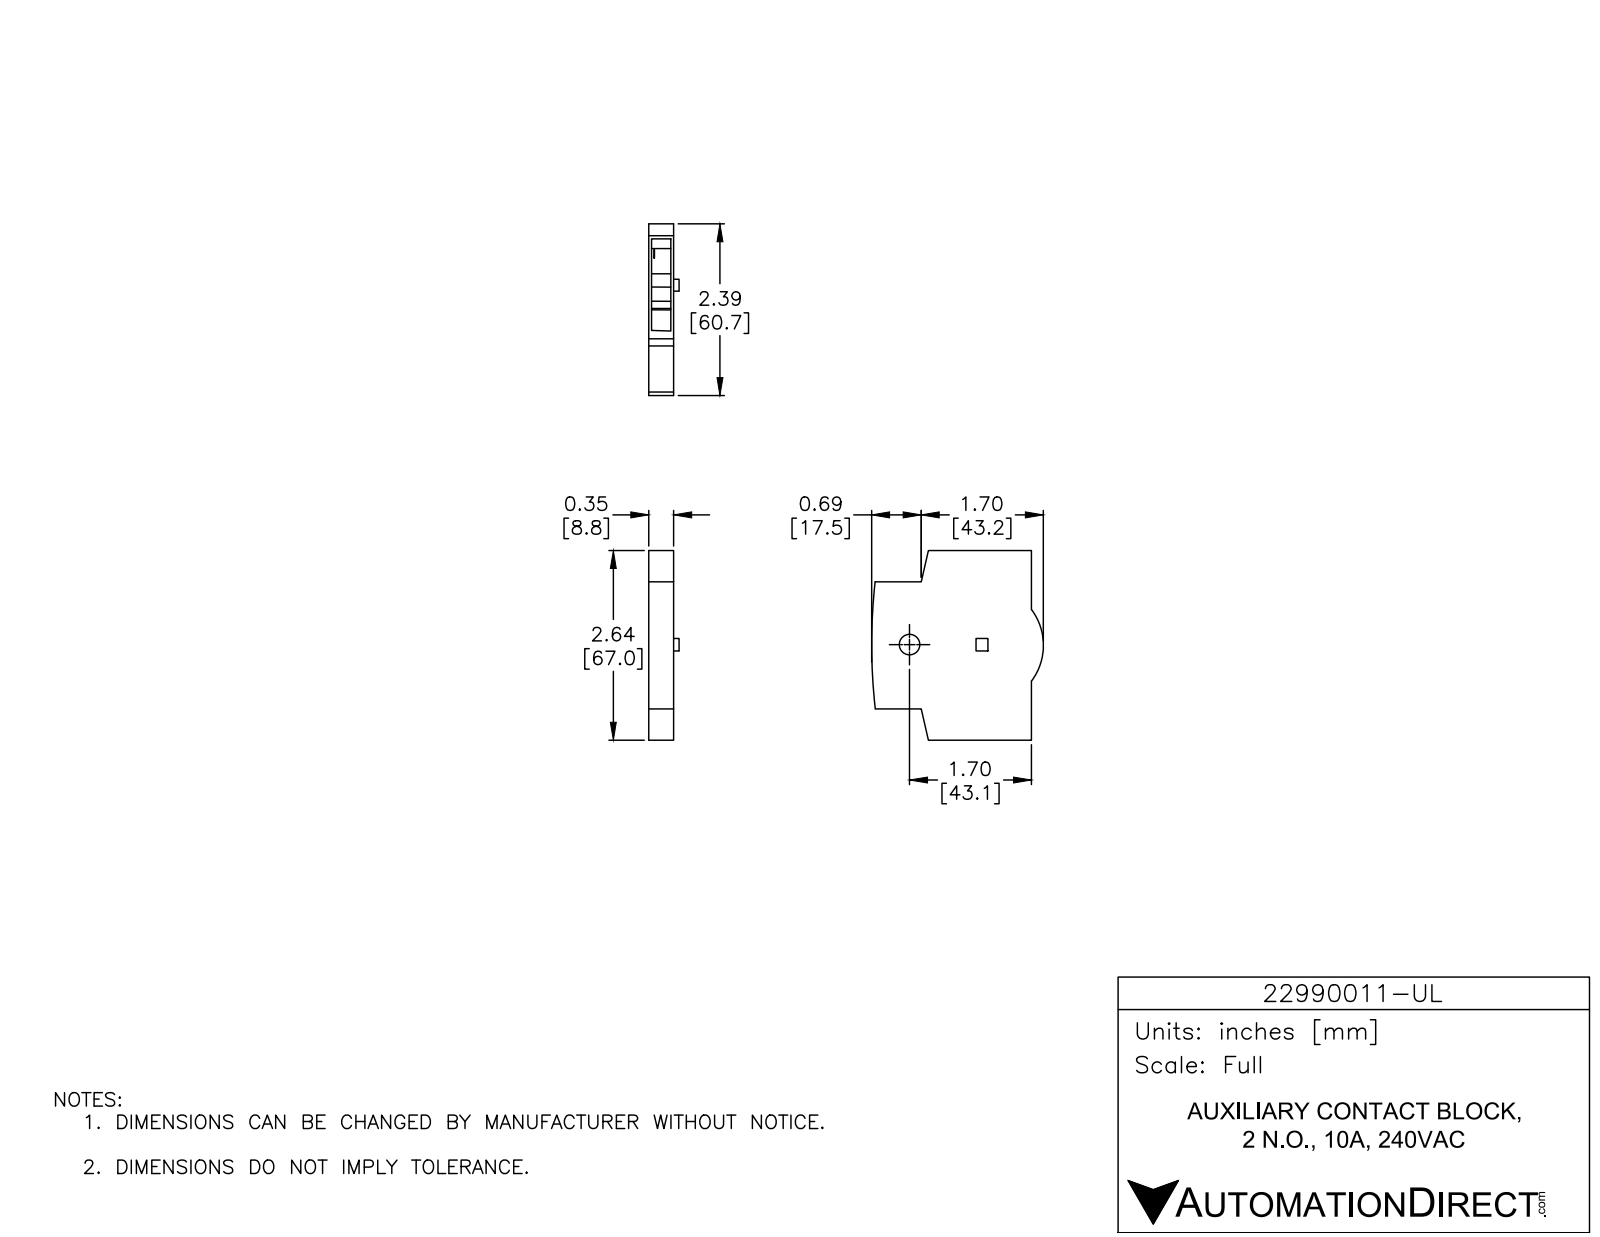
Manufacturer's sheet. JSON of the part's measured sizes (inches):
{"part_name": "22990011-UL", "step_written_by": "SolidWorks 2015 (AUTOMOTIVE_DESIGN)", "units": "inches", "bodies": {"solids": 1, "faces": 56, "planar": 52, "cylindrical": 1, "other": 3}, "overall_size": [2.638, 2.389, 0.421], "volume_in3": 1.679, "surface_area_in2": 16.01, "partial_cylinders_radius": [[0.827, 1]], "face_to_face_distances": [0.346, 0.039, 0.307, 0.268, 0.435, 2.203, 1.768, 2.638, 0.771, 0.369]}
